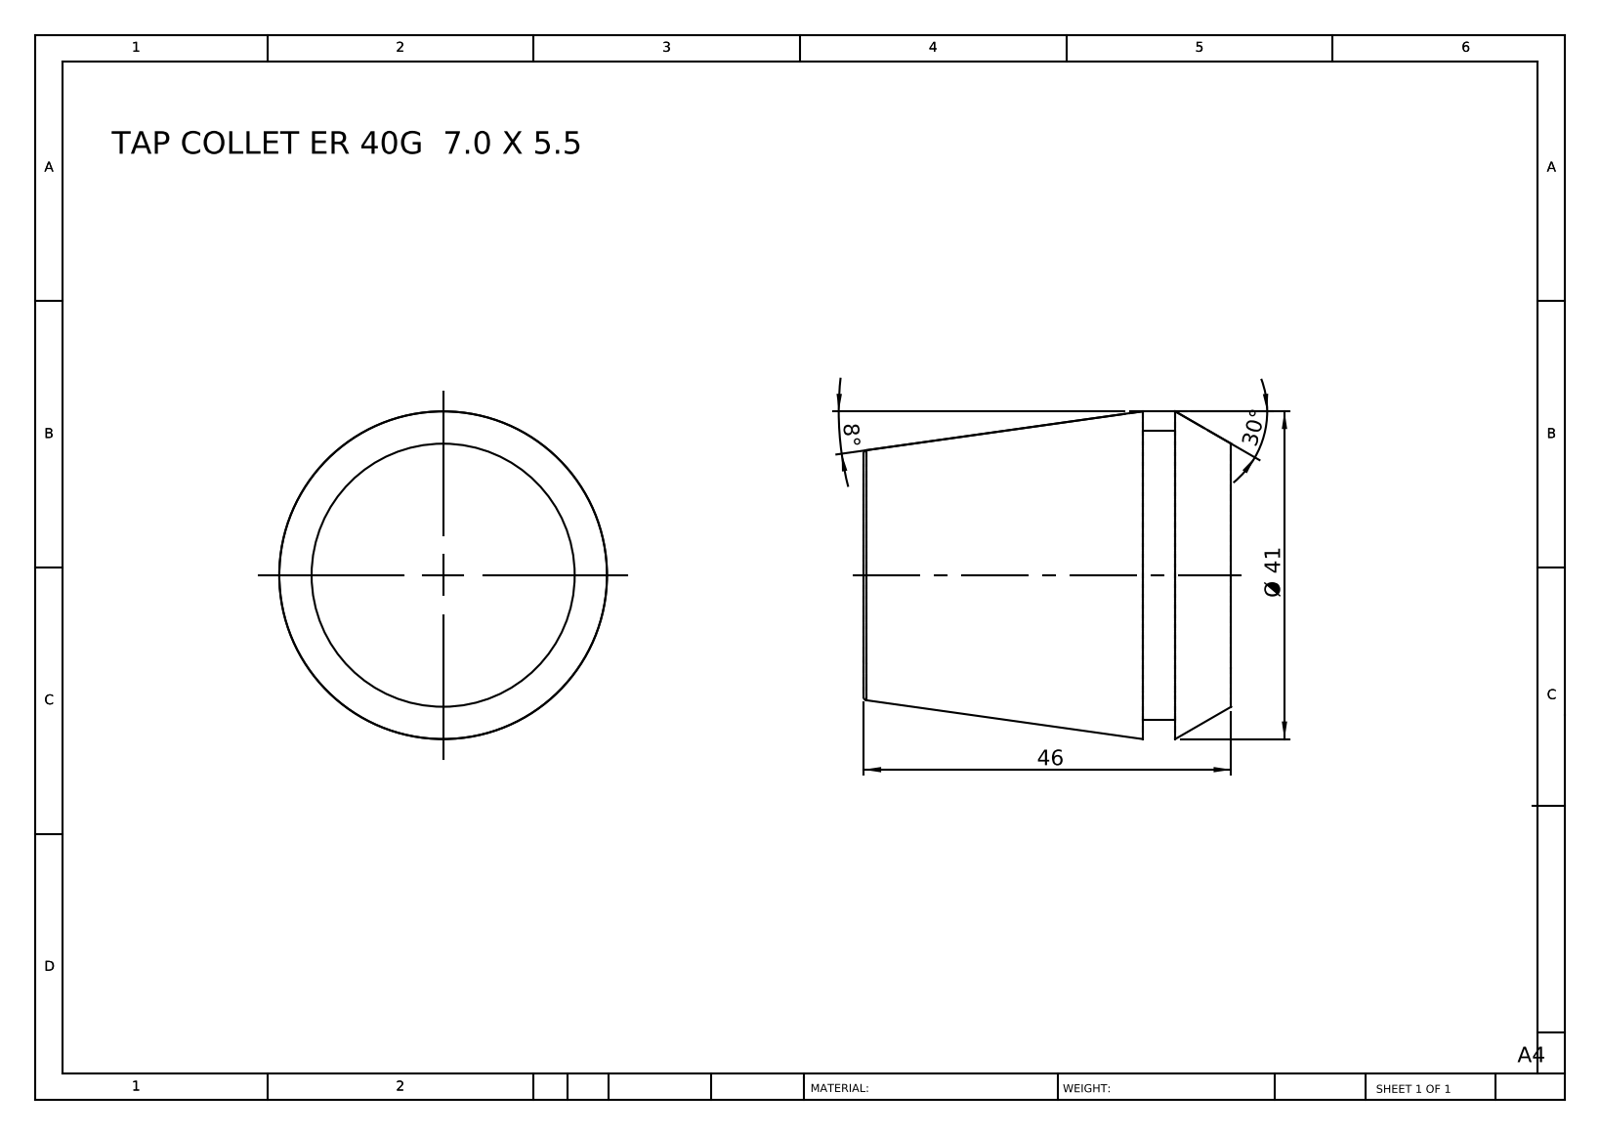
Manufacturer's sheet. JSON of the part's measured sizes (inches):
{"part_name": "TAP COLLET ER 40G 7.0 X 5.5", "step_written_by": "SolidWorks 2014 (CONFIG_CONTROL_DESIGN)", "units": "inches", "bodies": {"solids": 1, "faces": 12, "planar": 4, "cylindrical": 2, "other": 6}, "overall_size": [1.811, 1.614, 1.614], "volume_in3": 2.91, "surface_area_in2": 11.76, "round_bosses_or_shafts": [[1.425, 1]], "face_to_face_distances": [1.811, 0.437, 1.374, 0.276, 0.161, 1.535]}
